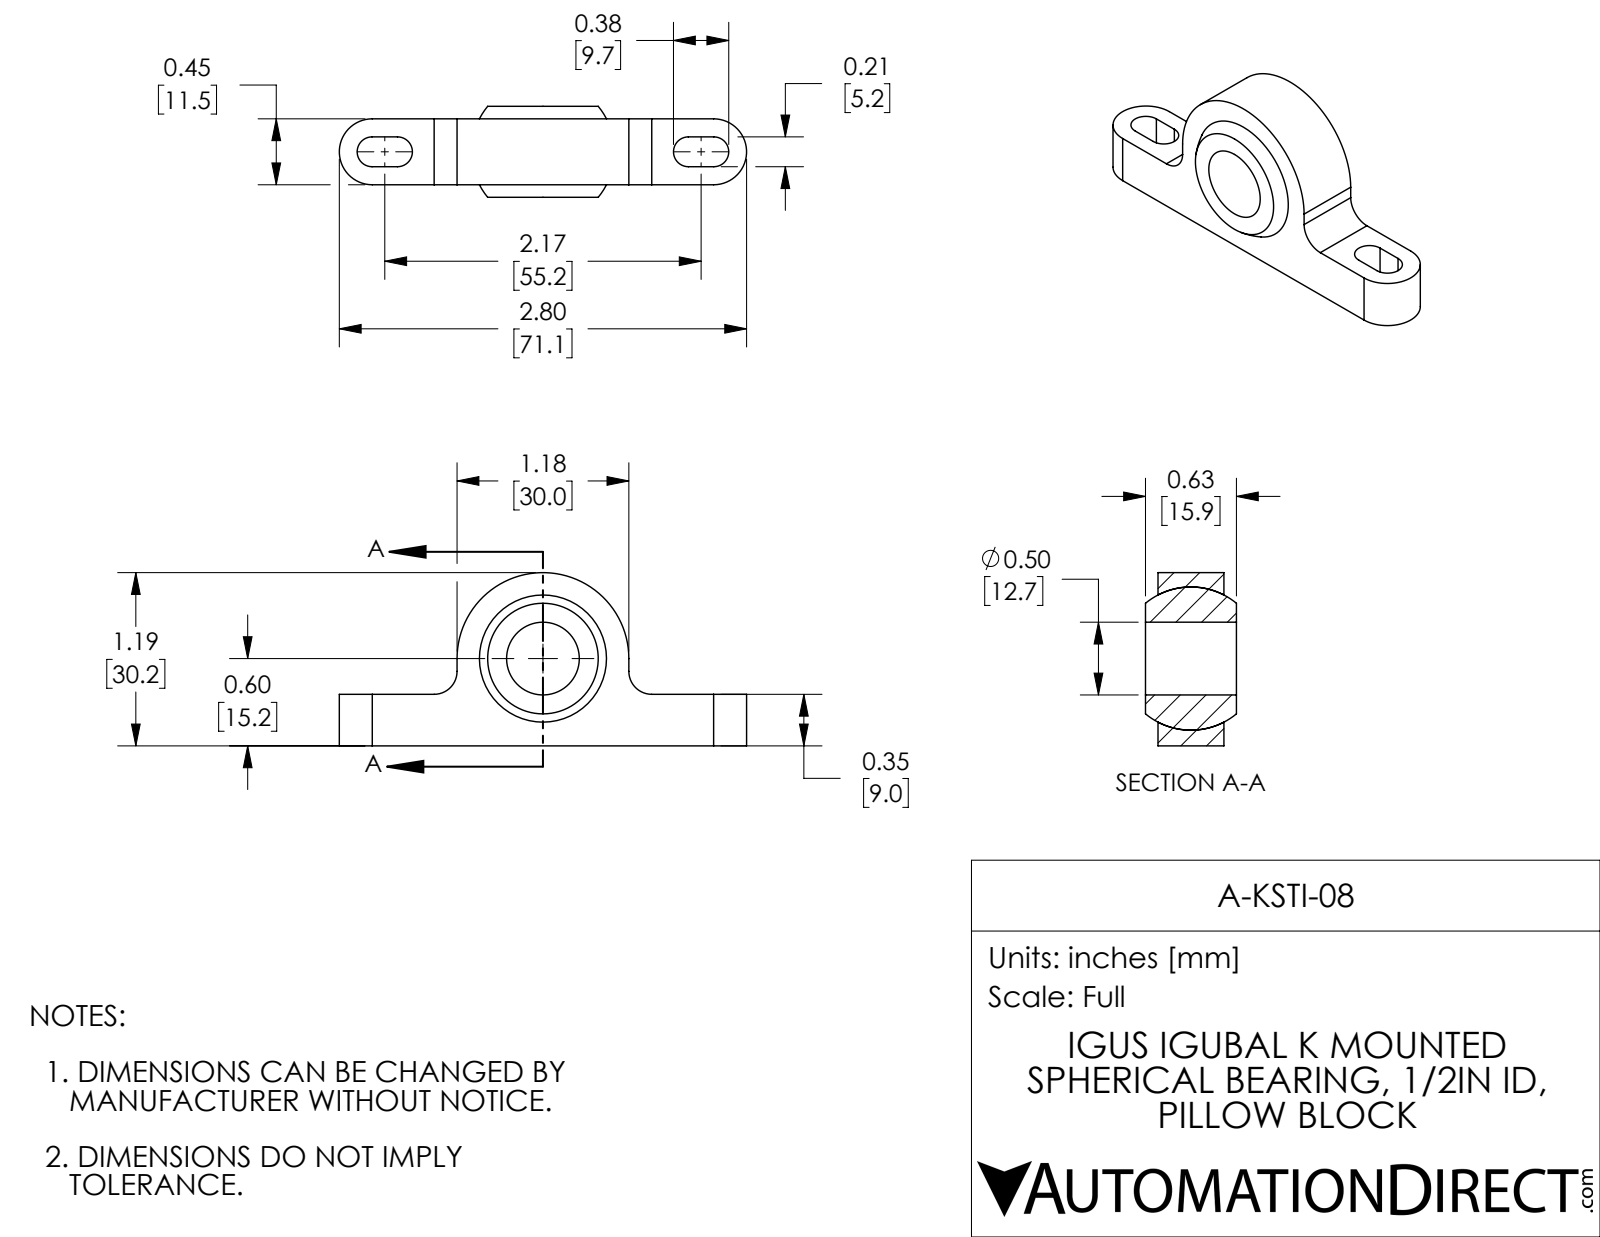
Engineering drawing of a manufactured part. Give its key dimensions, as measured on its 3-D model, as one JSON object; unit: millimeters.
{"part_name": "A-KSTI-08", "step_written_by": "SolidWorks 2017 (AUTOMOTIVE_DESIGN)", "units": "millimeters", "bodies": {"solids": 2, "faces": 31, "planar": 13, "cylindrical": 14, "other": 4}, "overall_size": [71.1, 30.3, 15.9], "volume_mm3": 12100, "surface_area_mm2": 6994, "round_holes": [[12.7, 1]], "partial_cylinders_radius": [[2.6, 4], [4, 2], [5.8, 2], [15, 1]], "face_to_face_distances": [11.5, 2.2, 13.7, 9, 15.9, 5.3, 10.5, 3.1, 8.4, 5.2]}
